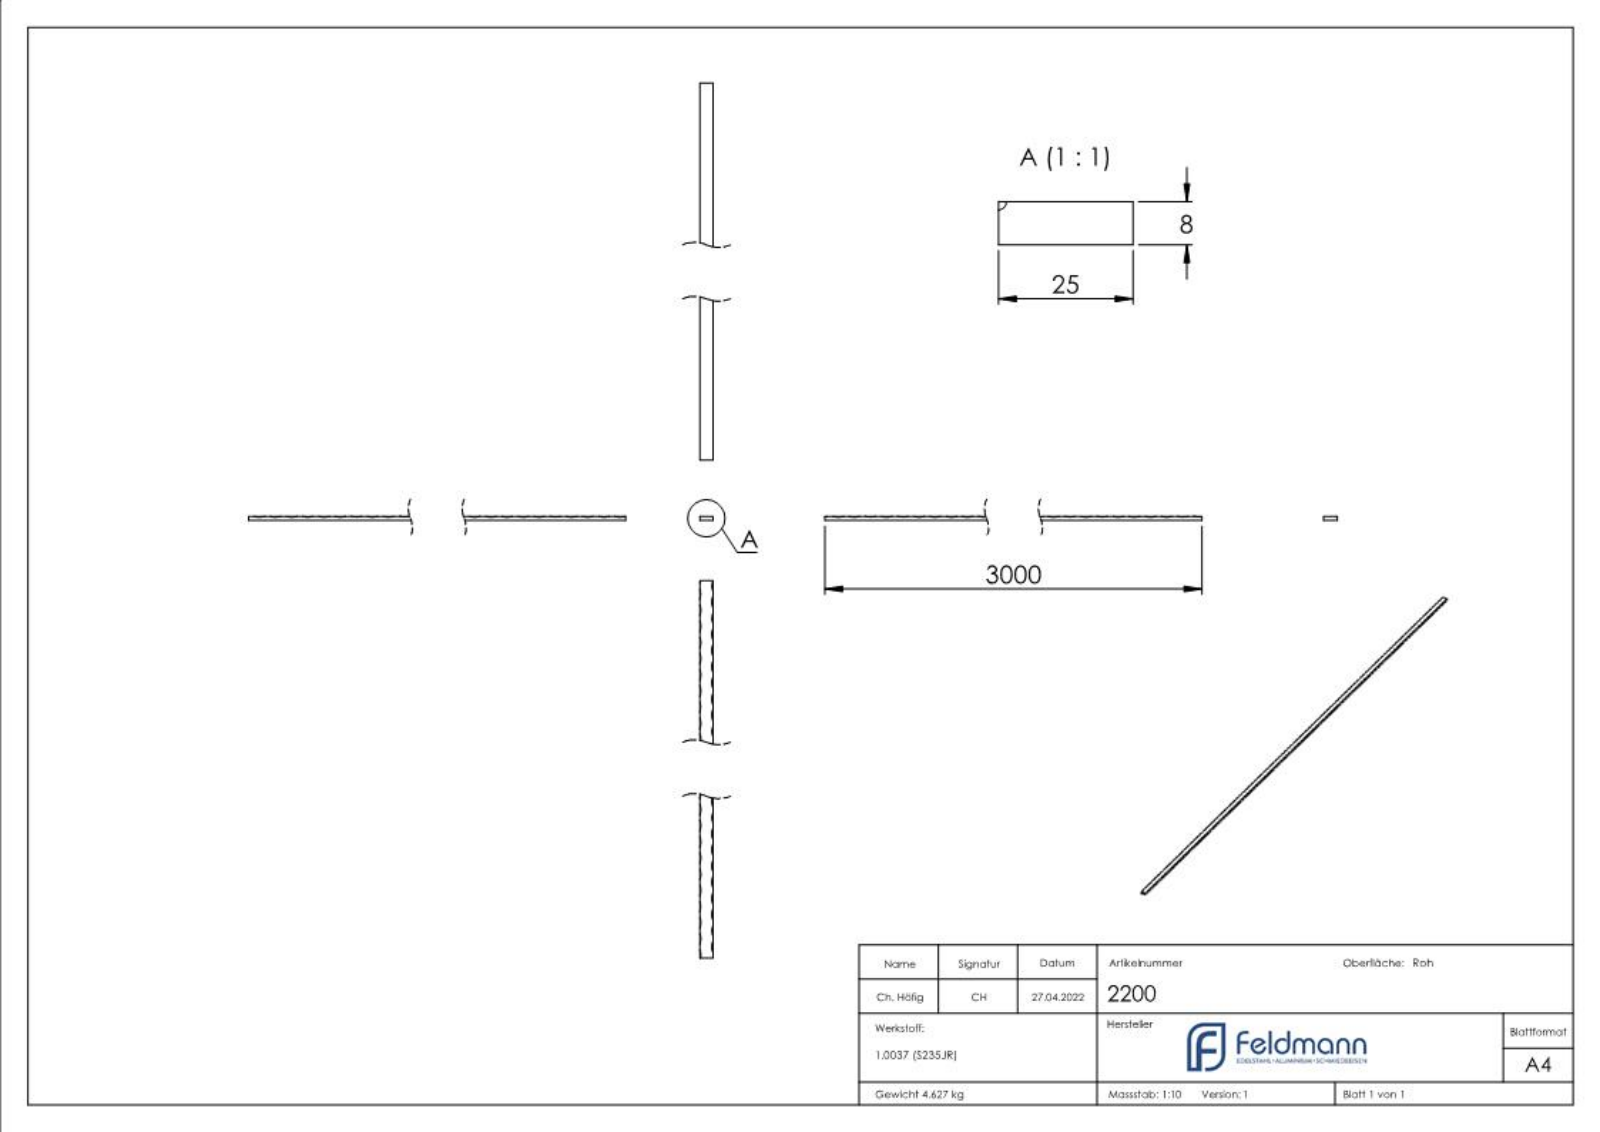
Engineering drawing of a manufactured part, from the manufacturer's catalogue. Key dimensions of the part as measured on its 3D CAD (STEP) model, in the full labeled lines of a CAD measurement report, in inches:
Part name (STEP PRODUCT): 2200
STEP written by: SolidWorks 2018 (CONFIG_CONTROL_DESIGN)
Units: inches
Bodies: 1 solid, 411 faces (112 planar, 0 cylindrical, 299 other)
Overall size (bounding box): 118.11 × 0.984 × 0.315
Volume: 36.2 in³ · Surface area: 304.2 in²
Main face-to-face distances: 0.315, 0.984, 118.11, 0.311, 0.144, 0.013, 59.055, 0.452, 0.532, 0.013
